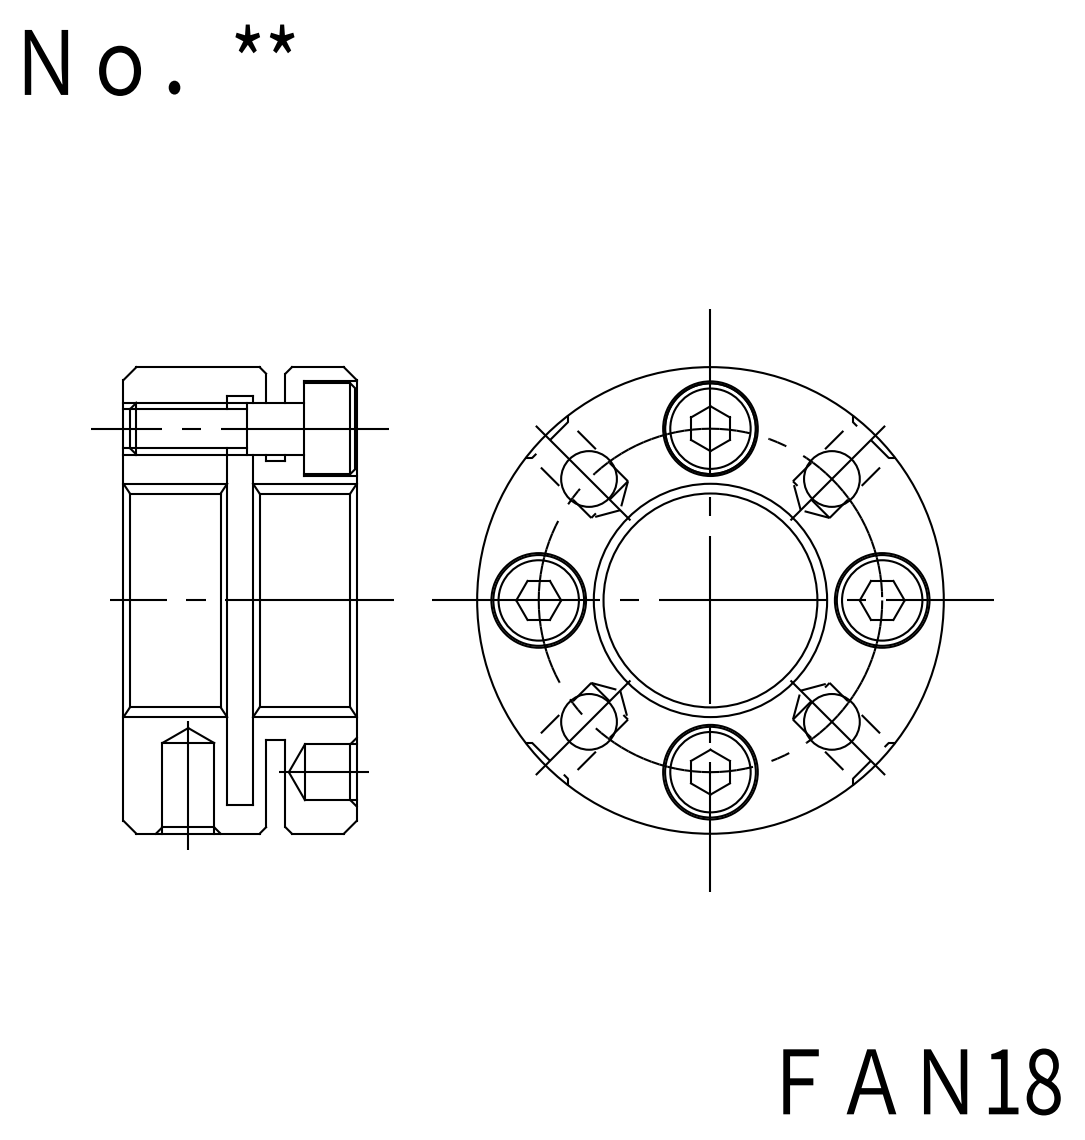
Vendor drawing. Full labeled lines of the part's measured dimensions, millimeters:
Part name (STEP PRODUCT): FKD FAN18; M4X12_default
STEP written by: SolidWorks 2012 (CONFIG_CONTROL_DESIGN)
Units: millimetres
Bodies: 5 solids, 142 faces (50 planar, 76 cylindrical, 16 other)
Overall size (bounding box): 36 × 36 × 18
Volume: 11 135 mm³ · Surface area: 9 403 mm²
Round holes (diameter × count): ⌀3.24 ×4, ⌀4.3 ×4, ⌀4.5 ×4, ⌀7.3 ×4, ⌀4 ×2, ⌀18 ×1, ⌀31.5 ×1
Round bosses / shafts (diameter × count): ⌀7 ×4, ⌀4 ×4, ⌀36 ×1, ⌀21.5 ×1
Main face-to-face distances: 8, 10, 11, 12.5, 1.5, 18, 7, 5.5, 2, 3
Hole centre spacings: 10.14, 13.25, 18.74, 24.48, 26.5
